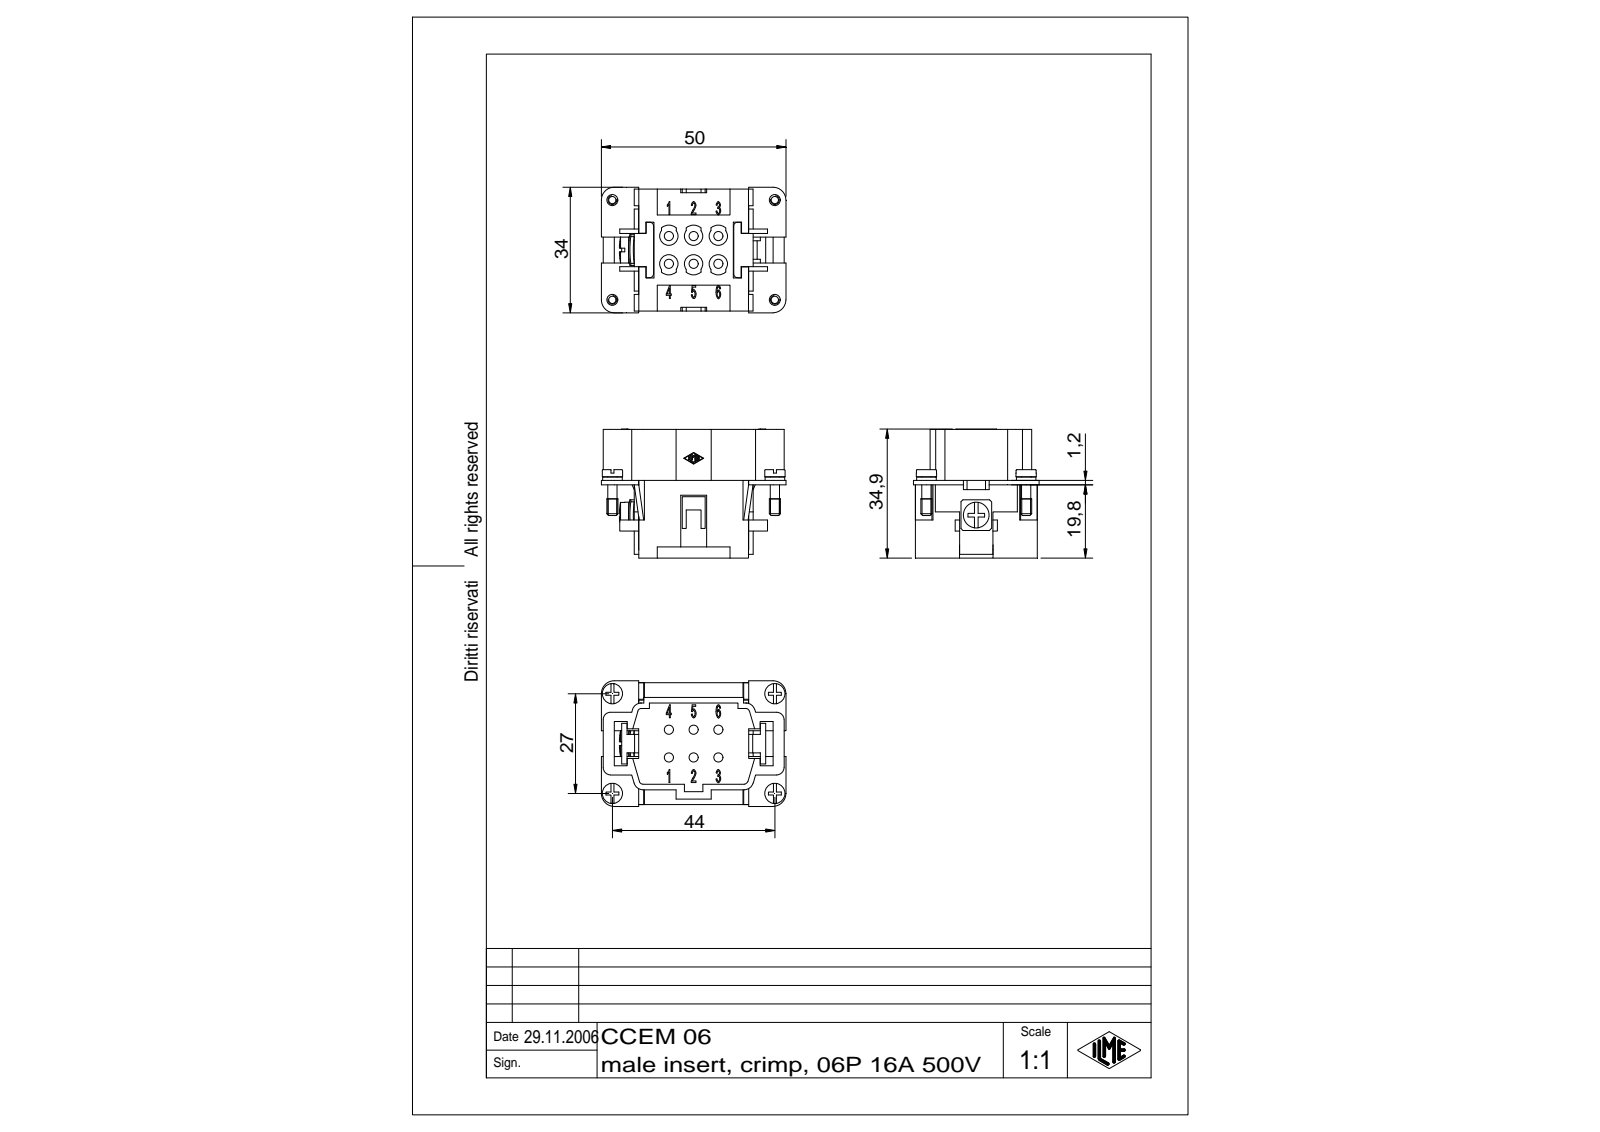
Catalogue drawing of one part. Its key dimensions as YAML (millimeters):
part_name: "CCEM 06"
step_written_by: "Autodesk Inventor 7 (AUTOMOTIVE_DESIGN)"
units: millimeters
bodies: {solids: 1, faces: 738, planar: 357, cylindrical: 81, other: 300}
overall_size: [50, 34.9, 34]
volume: 23476
surface_area: 15855
round_holes:
  - {diameter: 2.5, count: 3}
  - {diameter: 2.55, count: 2}
  - {diameter: 3.24, count: 1}
round_bosses_or_shafts:
  - {diameter: 5.5, count: 2}
  - {diameter: 5.3, count: 2}
  - {diameter: 3, count: 2}
  - {diameter: 2.5, count: 2}
  - {diameter: 7, count: 1}
partial_cylinders:
  - {radius: 0.1, count: 14}
  - {radius: 2.5, count: 7}
  - {radius: 1, count: 6}
  - {radius: 2, count: 6}
  - {radius: 3, count: 3}
  - {radius: 3.5, count: 2}
  - {radius: 5.5, count: 1}
face_to_face_distances: [1.5, 4, 22, 21, 3, 5.5, 27.5, 2.5, 1, 23.5]
hole_center_spacings: [6.7, 13.4, 18.14, 23.06, 24.06, 27, 27.96, 30.31]
